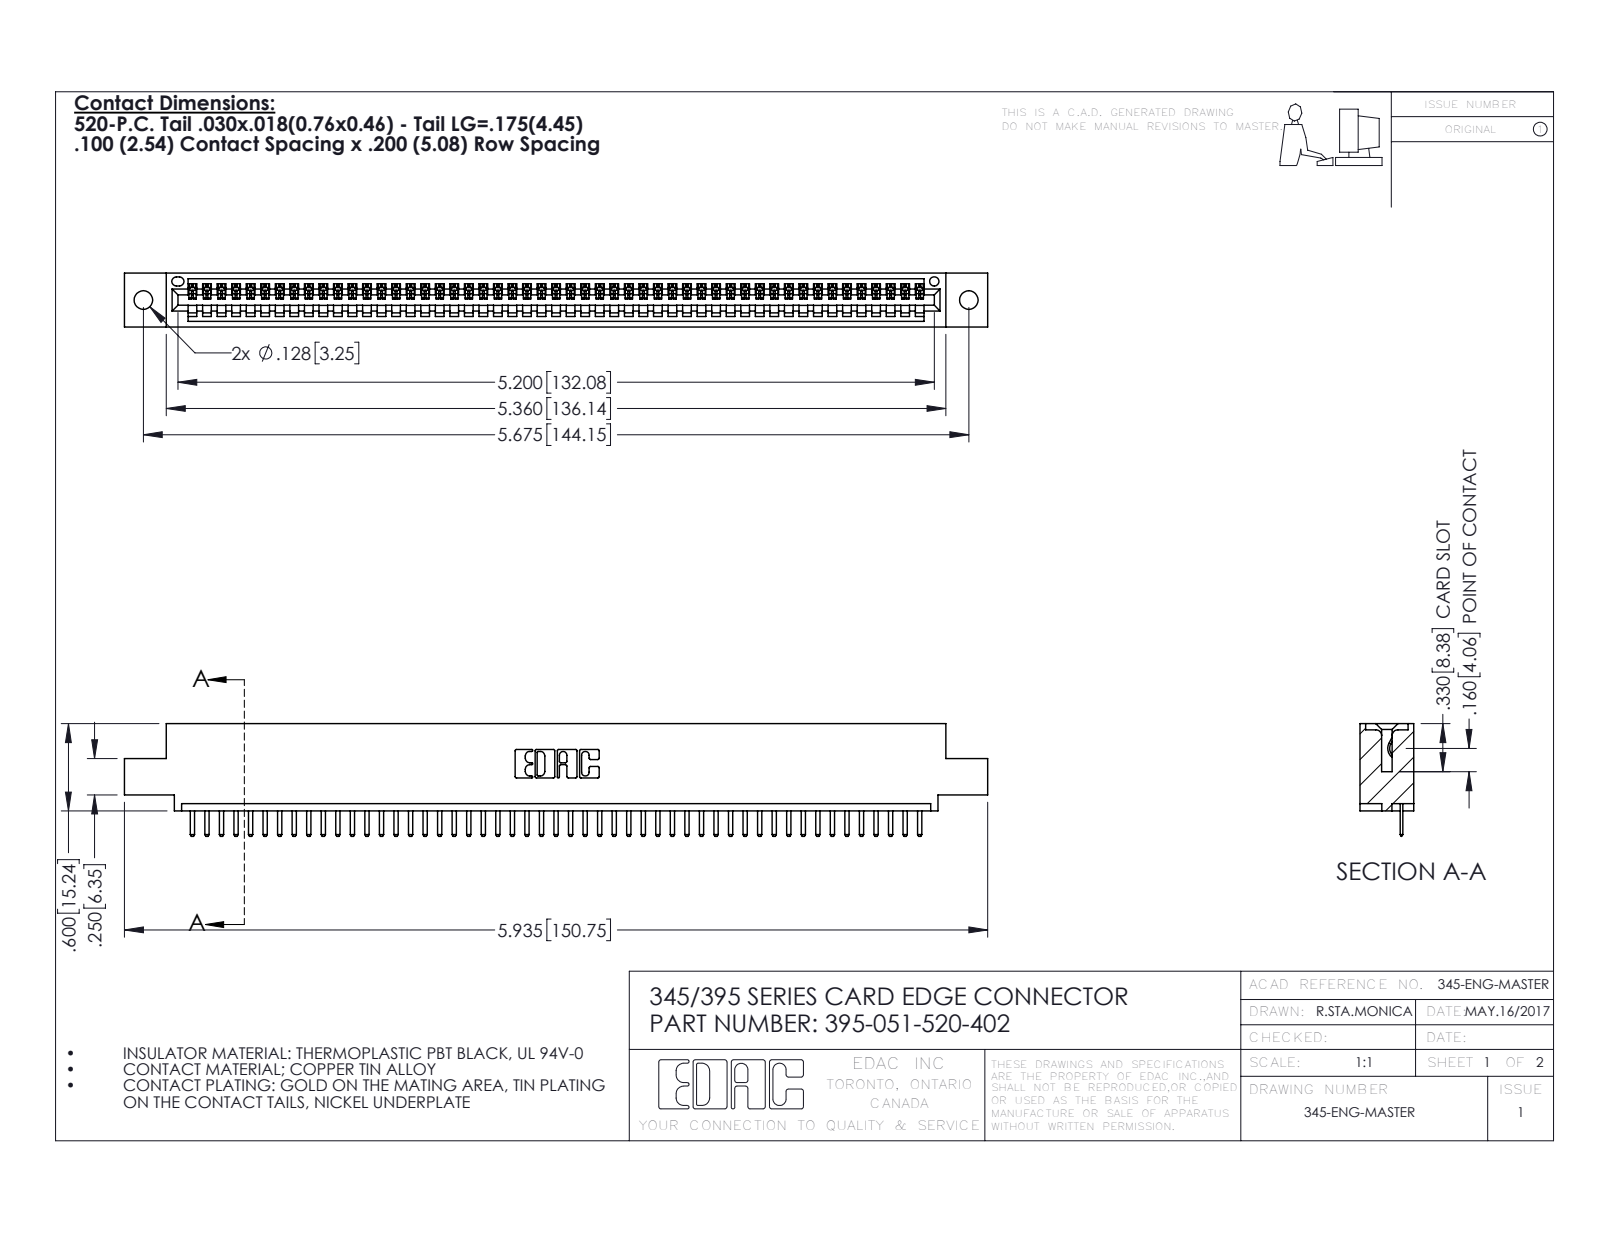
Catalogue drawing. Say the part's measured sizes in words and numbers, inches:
The part is named "395-051-520-402; 345 Part_0.110 Offset - 0.128 Dia; 345-292-001_345-293-120". Its 3-D file was written by "SolidWorks 2016 (CONFIG_CONTROL_DESIGN)". It is 52 solids with 3292 faces: 2226 planar, 1066 cylindrical and 0 other. Overall it measures 5.935 by 0.775 by 0.37 inches. Its volume is 0.863 cubic inches and its surface area 28.27 square inches. Round holes: 2 of diameter 0.128, 1 of diameter 0.064. Partial cylindrical surfaces (rounded edges, fillets, slot ends): 104 of radius 0.01, 102 of radius 0.006, 22 of radius 0.01, 6 of radius 0.007, 6 of radius 0.031, 3 of radius 0.026, 2 of radius 0.031, 2 of radius 0.04. The main face-to-face distances are 0.298, 0.072, 0.37, 0.2, 0.098, 0.272, 0.025, 0.225, 0.072, 0.149. The hole center spacings are 0.27, 5.439, 5.675.
